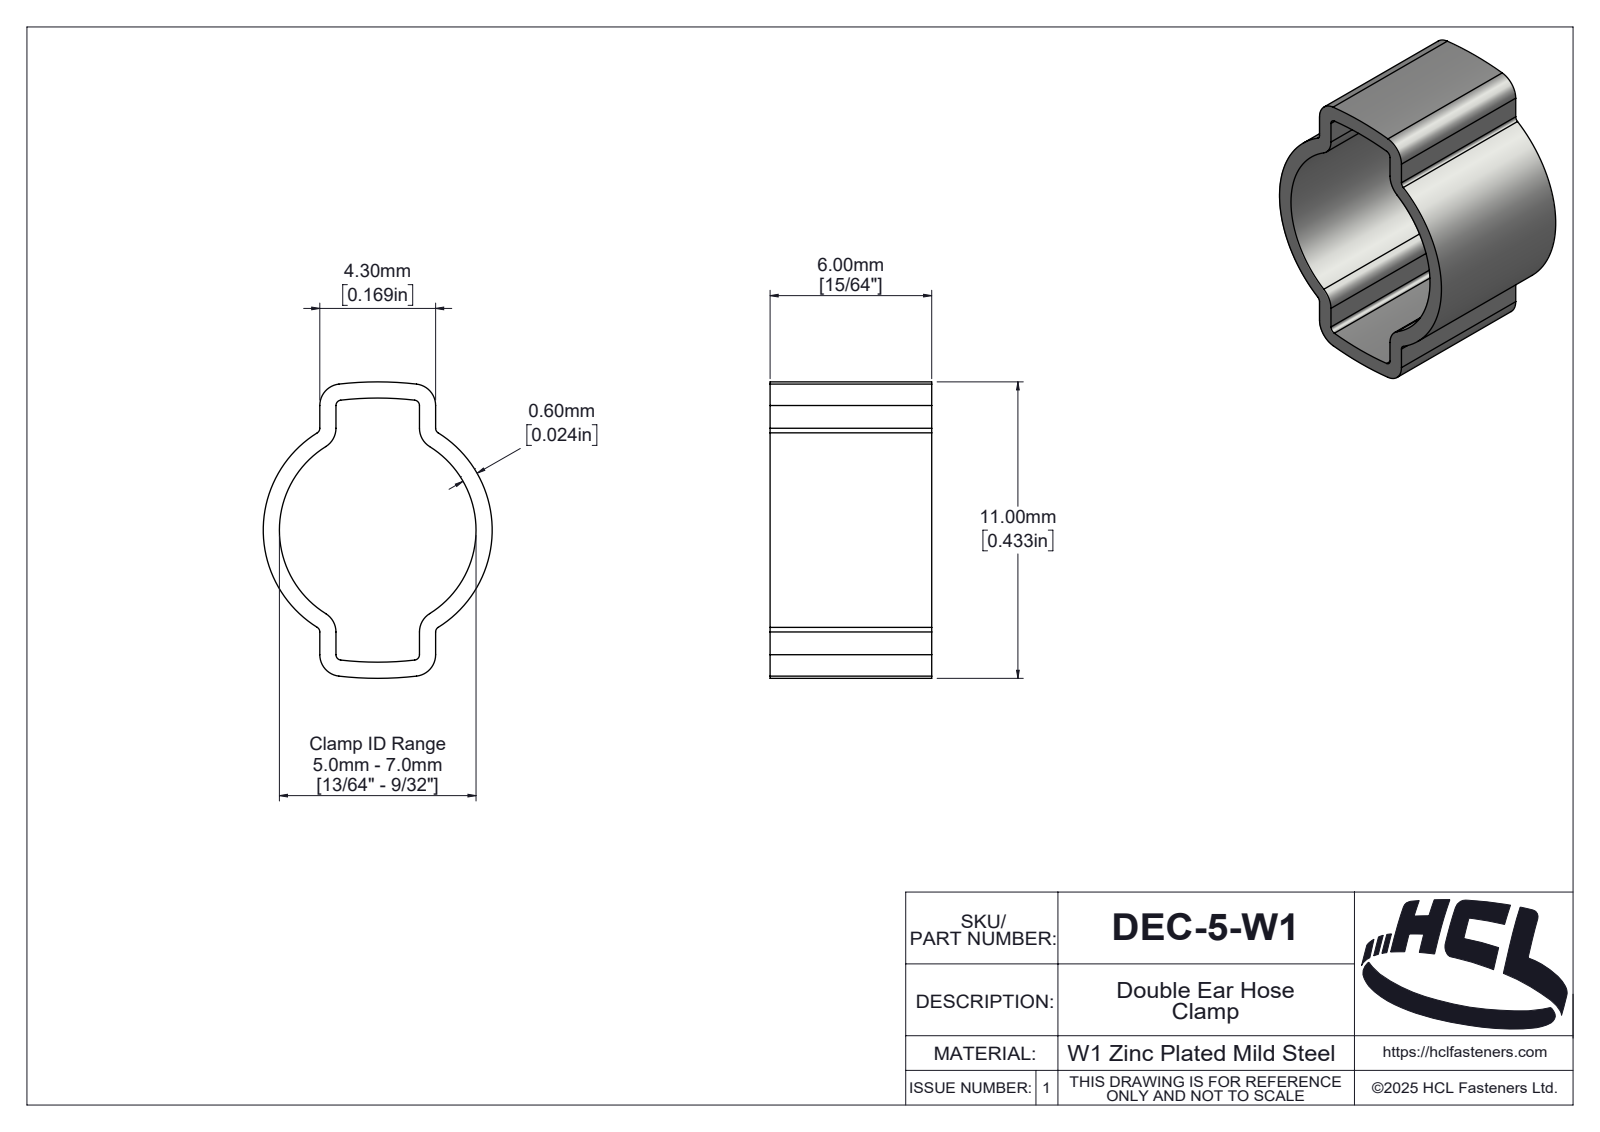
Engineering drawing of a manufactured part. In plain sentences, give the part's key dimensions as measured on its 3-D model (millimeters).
The part is named "DEC-5-W1". Its 3-D file was written by "SolidWorks 2025 (AUTOMOTIVE_DESIGN)". It is 1 solid with 137 faces: 12 planar, 76 cylindrical and 49 other. Overall it measures 11 by 8.5 by 6 millimeters. Its volume is 108 cubic millimeters and its surface area 398 square millimeters. Partial cylindrical surfaces (rounded edges, fillets, slot ends): 8 of radius 0.2, 8 of radius 0.8, 2 of radius 12.06, 2 of radius 12.66, 1 of radius 0.13, 1 of radius 0.54, 1 of radius 0.67, 1 of radius 0.71. The main face-to-face distances are 0.6, 3.7, 6, 4.3, 3.1, 1.97, 1.37, 1.73, 2.33, 2.07.
